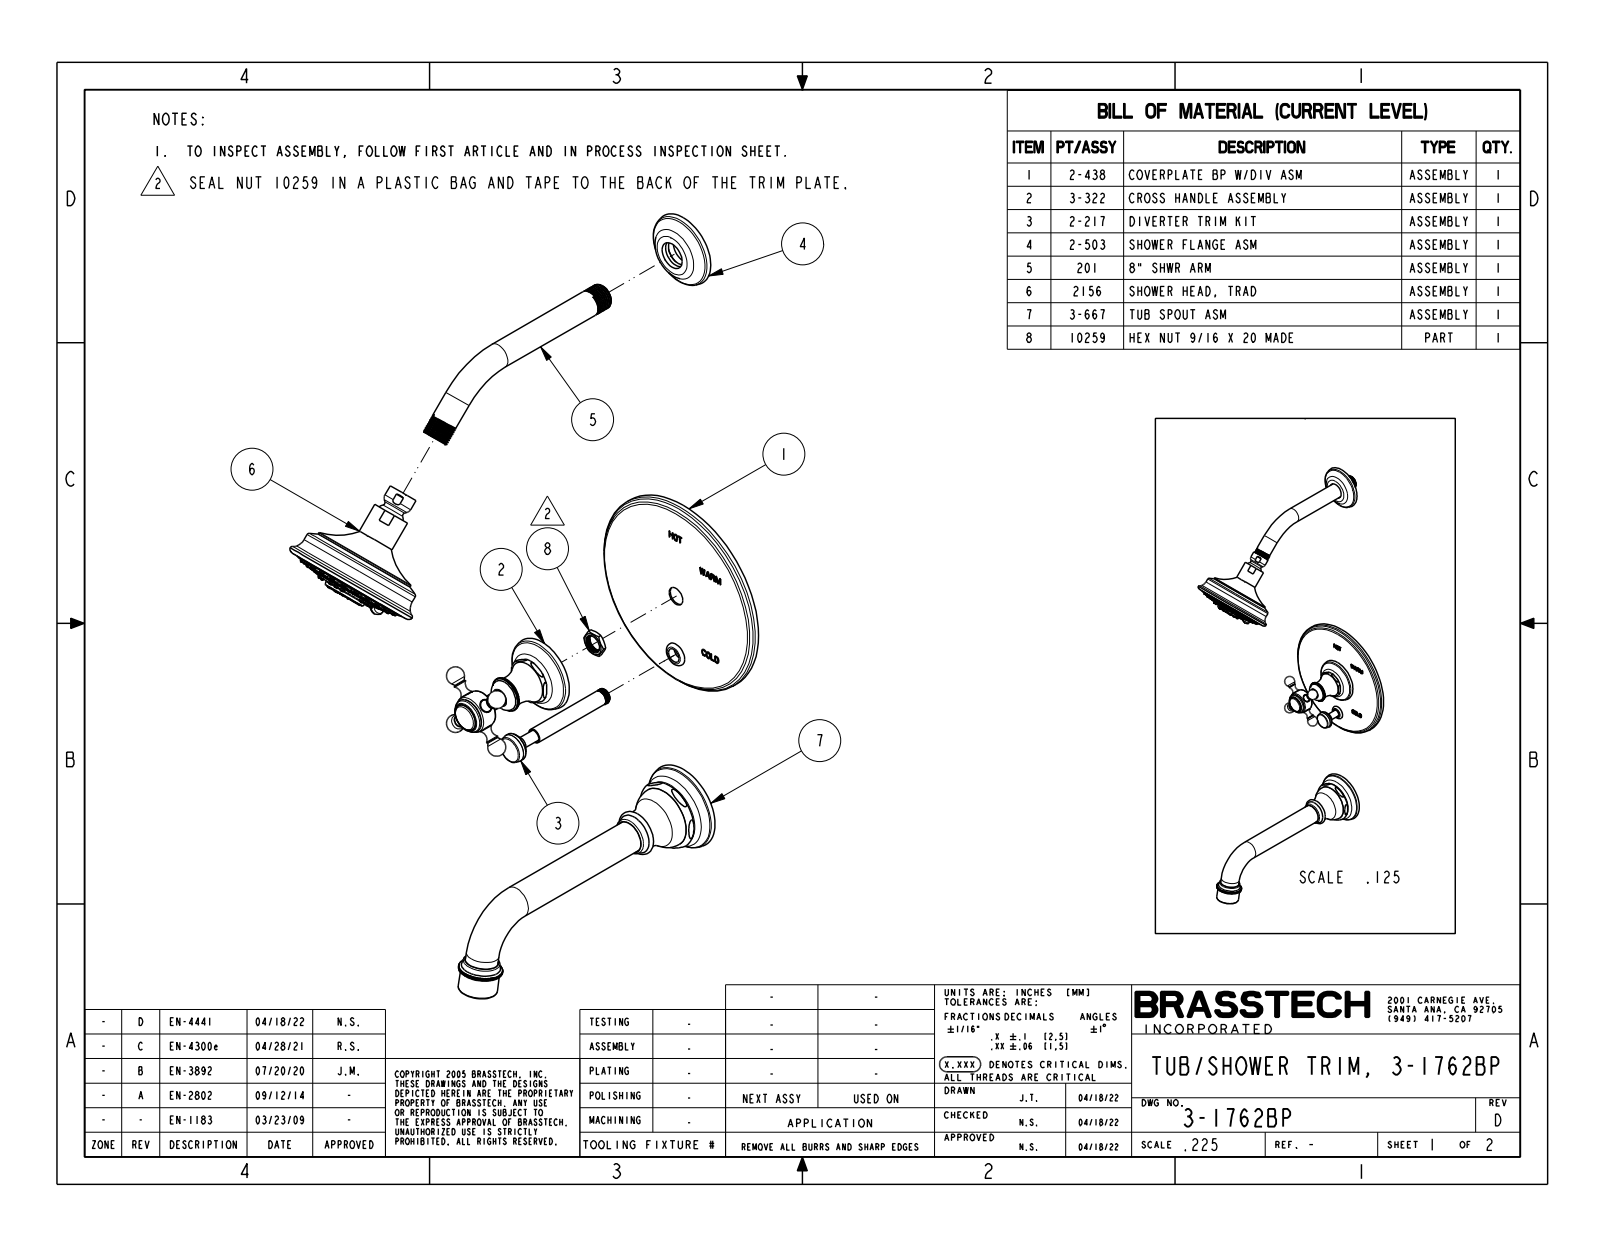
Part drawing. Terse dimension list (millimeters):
name: 3-1762BP
written by: CREO PARAMETRIC BY PTC INC, 2018400 (CONFIG_CONTROL_DESIGN)
unit: mm
bodies: 3 solids, 1827 faces (737 planar, 223 cylindrical, 867 other)
size: 623.8 × 255.3 × 165.1
volume: 792 000 mm³; area: 141 200 mm²
holes: 8× ⌀1.5, 2× ⌀10.4, 1× ⌀21.7, 1× ⌀23.5
bosses: 39× ⌀3.6, 23× ⌀4.2, 2× ⌀25.4, 2× ⌀20.7, 2× ⌀10, 1× ⌀165.1, 1× ⌀96.8, 1× ⌀94.6
rounds: 8× R2, 2× R0.5, 1× R3.5, 1× R12, 1× R13, 1× R16
face distances: 8, 12.2, 4.2, 1.6, 3, 4.6, 38.2, 30.3, 26, 72.5
hole spacings: 11.3, 14.7, 20.8, 20.8, 27.2, 11.3, 14.7, 27.2
